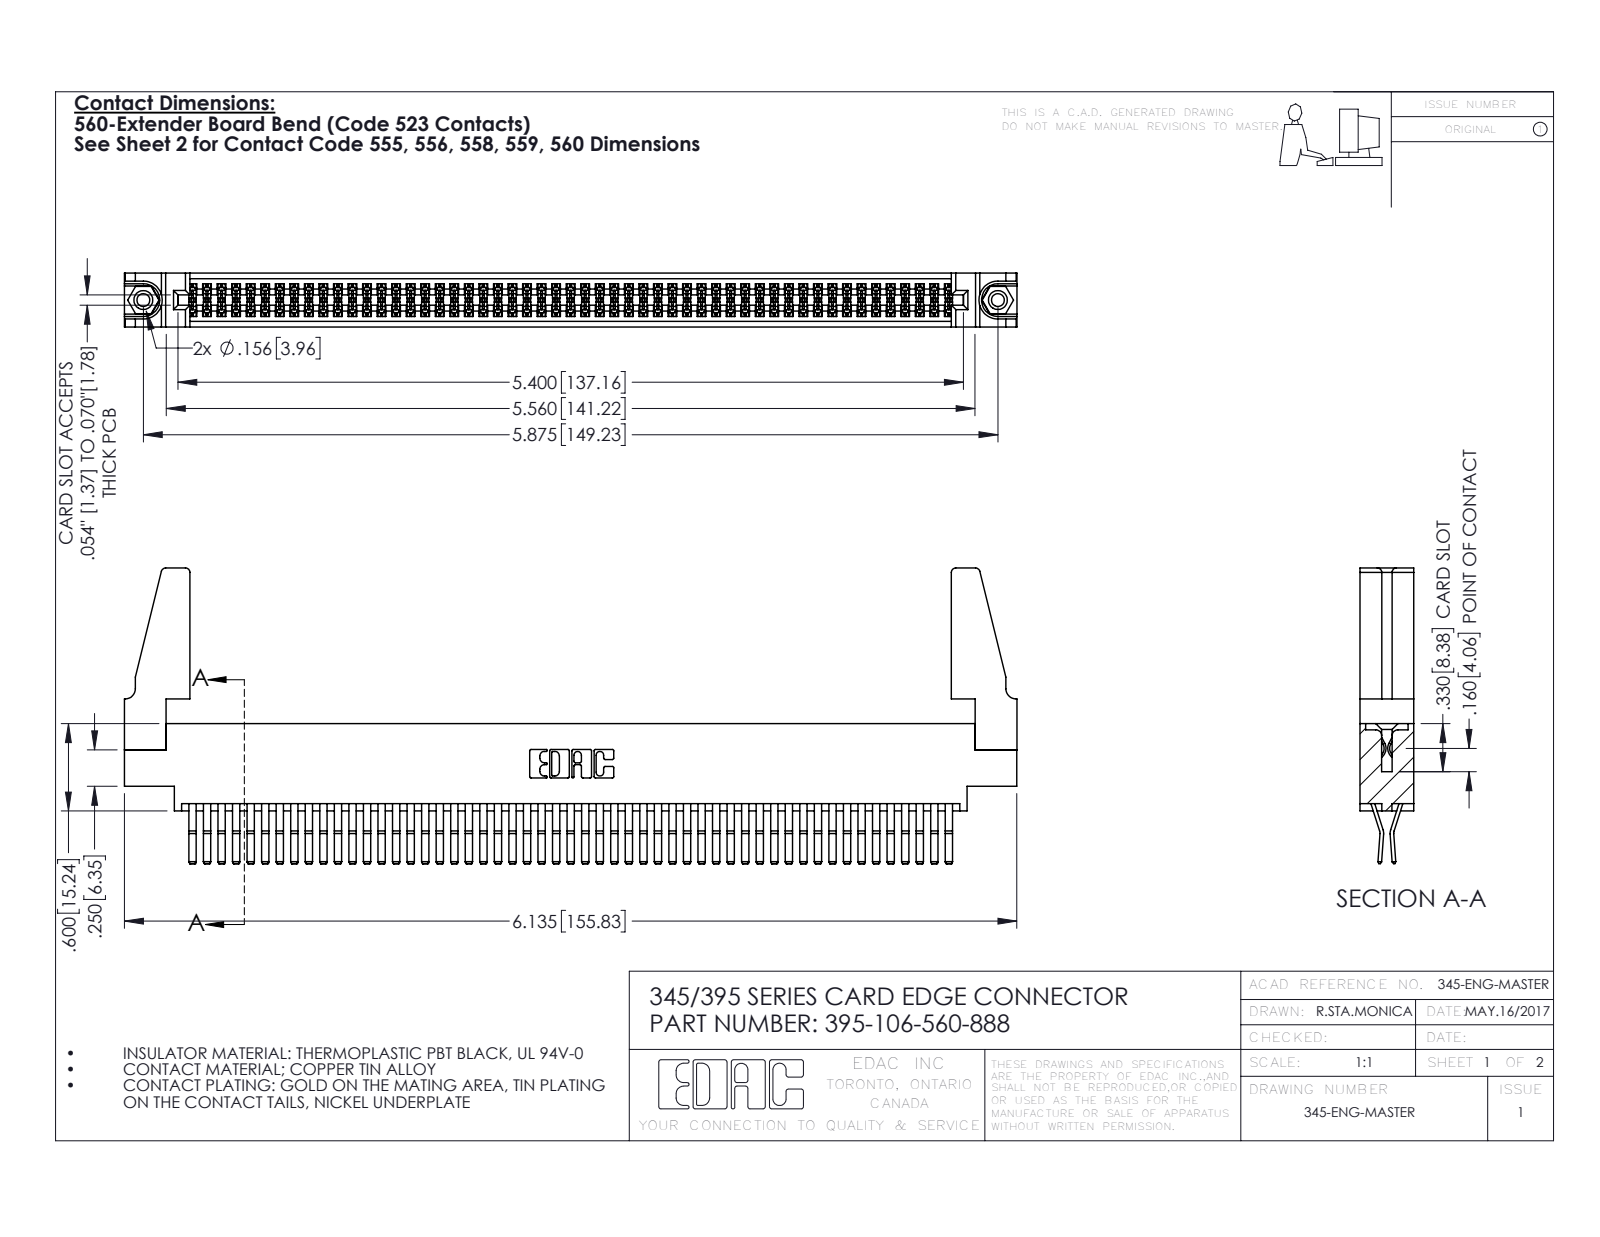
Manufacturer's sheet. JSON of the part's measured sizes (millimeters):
{"part_name": "395-106-560-888; 345-220-078_345-220-088; 345-292-001_560 Tail; 345-250-001_345-250-001-102 (+1 more)", "step_written_by": "SolidWorks 2016 (CONFIG_CONTROL_DESIGN)", "units": "millimeters", "bodies": {"solids": 111, "faces": 5766, "planar": 3654, "cylindrical": 2096, "other": 16}, "overall_size": [155.9, 51.6, 9.4], "volume_mm3": 19070, "surface_area_mm2": 28660, "round_holes": [[2.3, 2], [3.2, 2], [4, 2], [1.6, 1]], "round_bosses_or_shafts": [[3.9, 2]], "partial_cylinders_radius": [[0.2, 160], [0.3, 22], [0.8, 8], [0.2, 6], [0.8, 6], [0.7, 3], [0.3, 2], [0.4, 2]], "face_to_face_distances": [1.8, 7.6, 0.6, 9.4, 5.1, 2.5, 6.9, 5.7, 4.4, 3.8], "hole_center_spacings": [6.9, 143.2, 149.2]}
